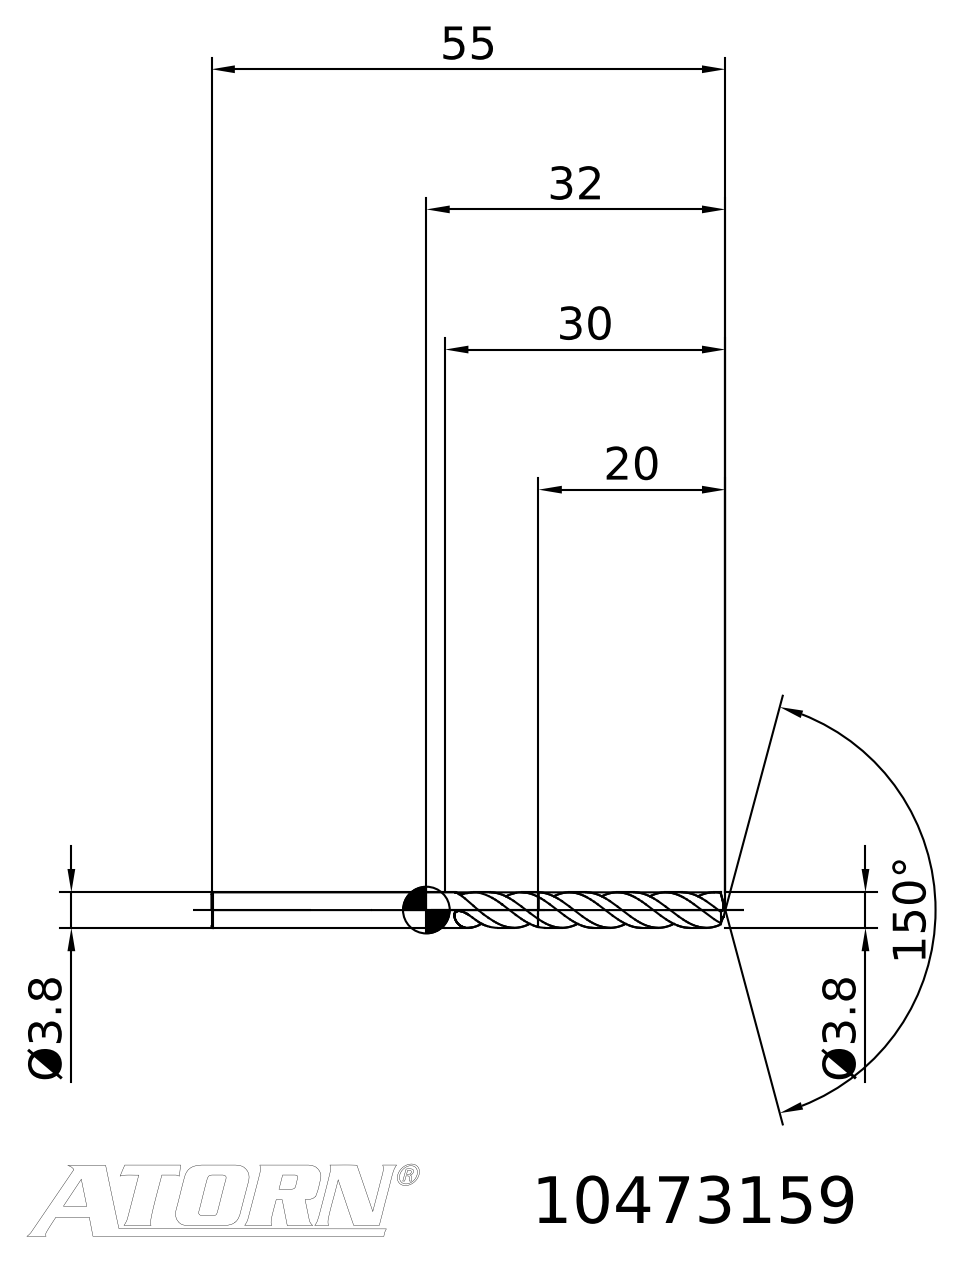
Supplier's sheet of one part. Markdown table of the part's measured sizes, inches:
| quantity | value |
| --- | --- |
| STEP written by | TDM (AUTOMOTIVE_DESIGN) |
| units | inches |
| bodies | 2 solids, 37 faces (3 planar, 0 cylindrical, 34 other) |
| overall size | 2.165 × 0.222 × 0.169 |
| volume | 0.028 in³ |
| surface area | 1.14 in² |
| main face-to-face distances | 1.378 |
